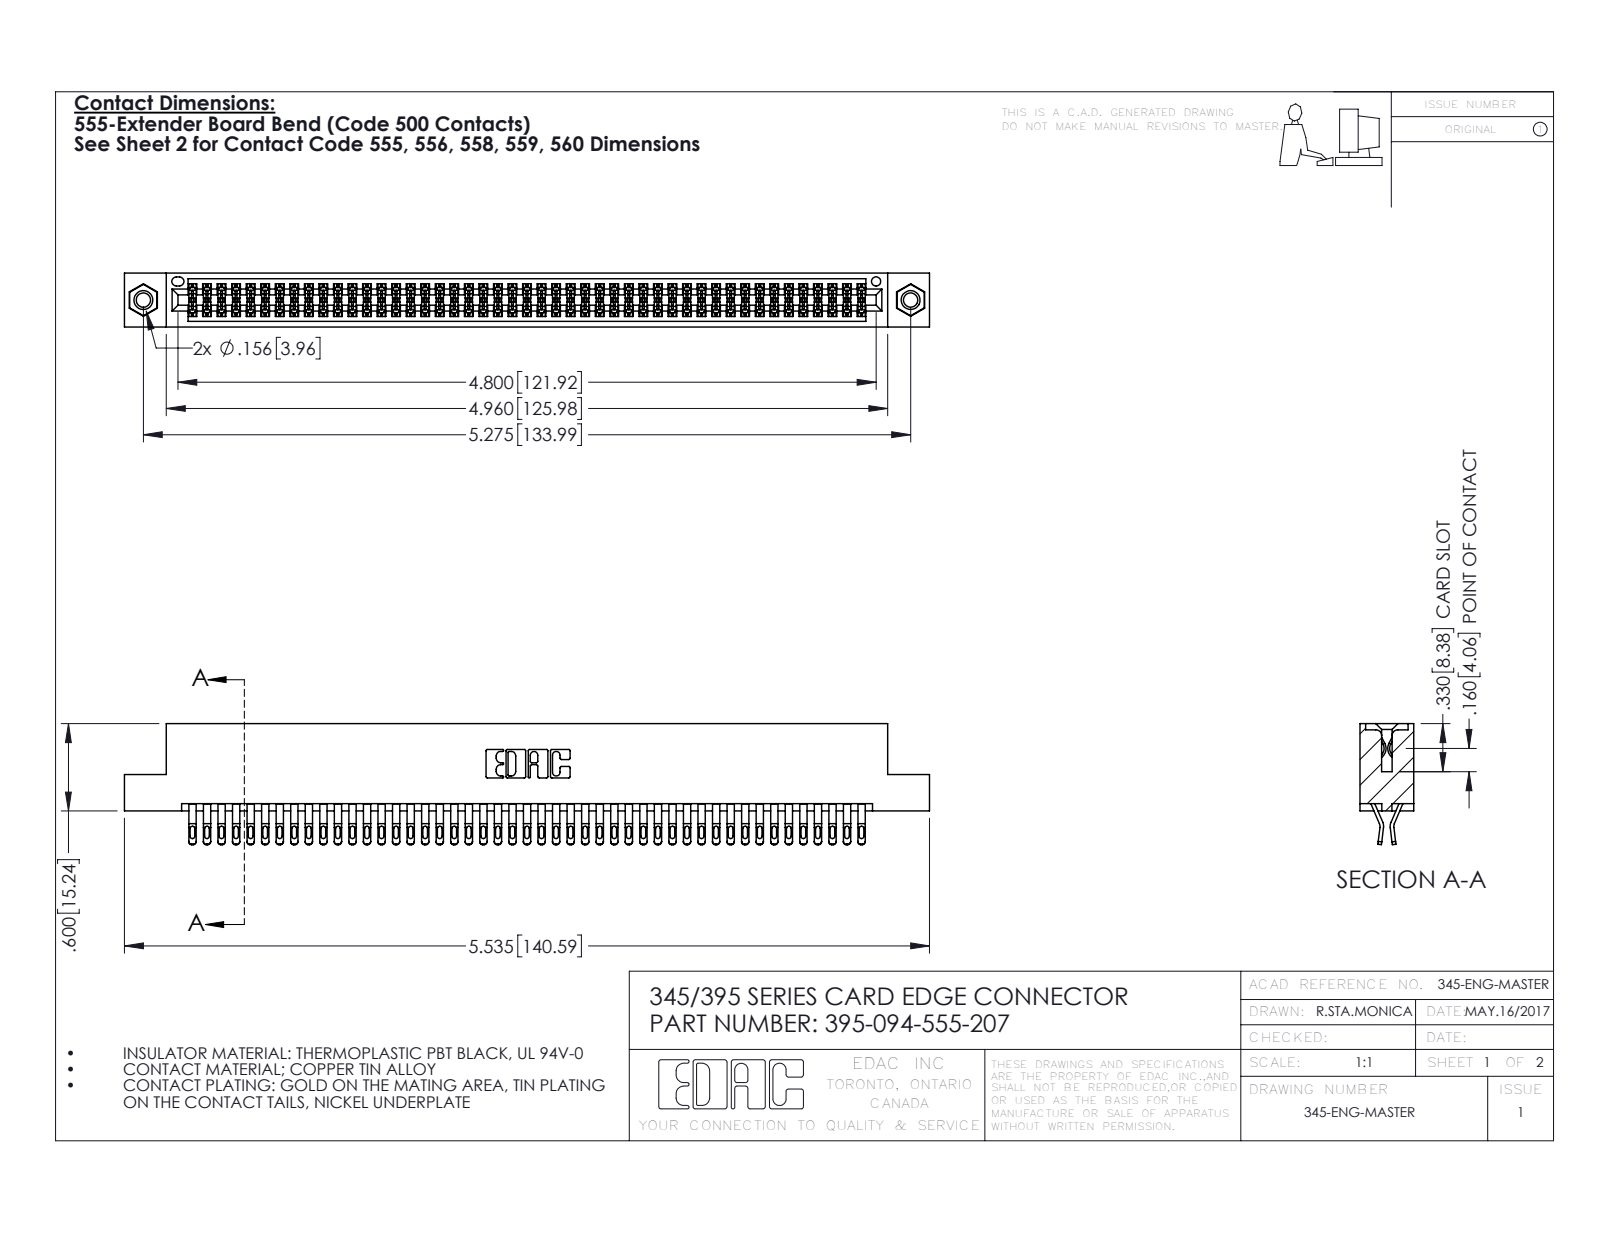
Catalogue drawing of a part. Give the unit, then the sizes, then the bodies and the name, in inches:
Units: inches
Overall size (bounding box): 5.535 × 0.832 × 0.37
Round holes (diameter × count): ⌀0.098 ×2, ⌀0.125 ×2, ⌀0.156 ×2, ⌀0.064 ×1
Round bosses / shafts (diameter × count): ⌀0.155 ×2
Partial cylindrical surfaces — rounded edges, fillets, slot ends (radius × count): R0.016 ×235, R0.02 ×188, R0.006 ×141, R0.01 ×22, R0.007 ×6, R0.031 ×6, R0.026 ×3, R0.01 ×2
Main face-to-face distances: 0.072, 0.298, 0.025, 0.2, 0.37, 0.098, 0.272, 0.225, 0.175, 0.149
Hole centre spacings: 0.27, 5.039, 5.275
Volume: 0.852 in³ · Surface area: 33.65 in²
Bodies: 97 solids, 5450 faces (3026 planar, 2408 cylindrical, 16 other)
Part name (STEP PRODUCT): 345-292-001_555 Tail; 345 Part_Flush Mounting Lugs - 0.156 Dia-TI; 395-094-555-207; 345-250-001_345-250-005-103
STEP written by: SolidWorks 2016 (CONFIG_CONTROL_DESIGN)
